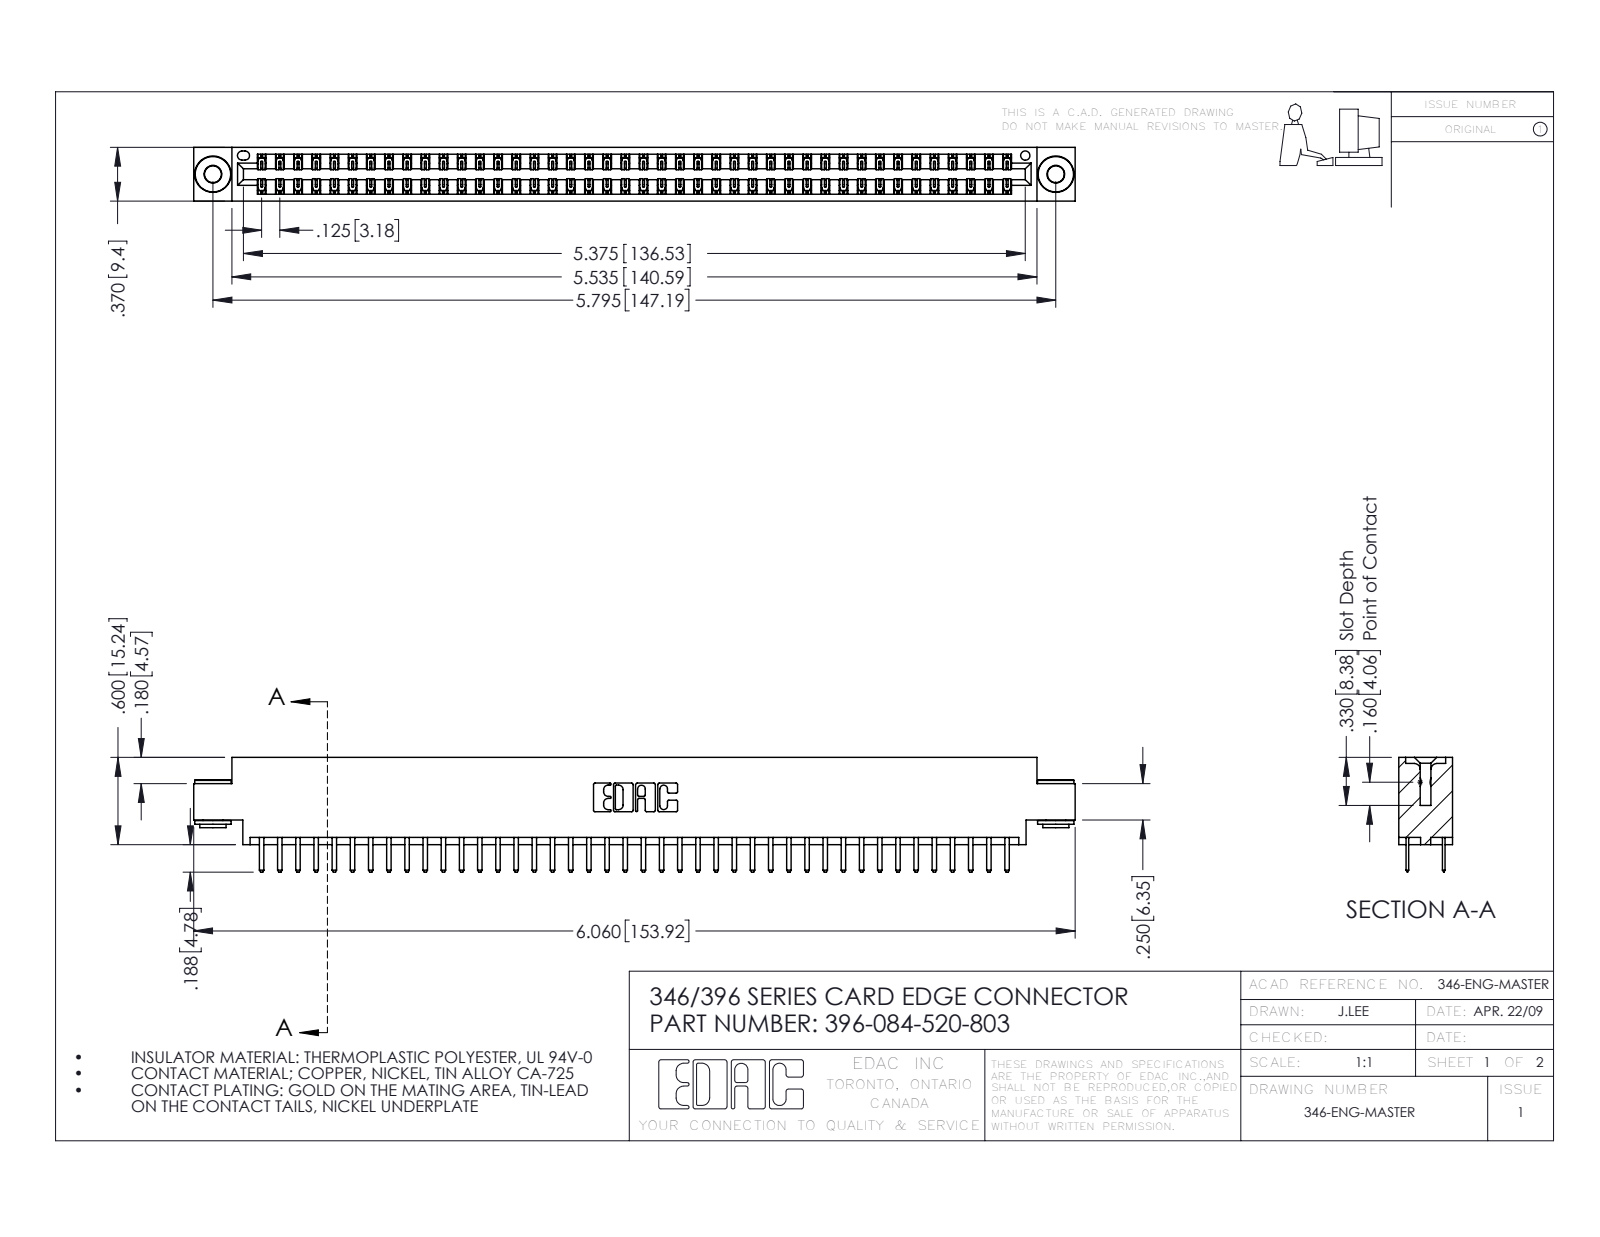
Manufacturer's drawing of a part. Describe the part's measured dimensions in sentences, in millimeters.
The part is named "345-250-002_345-250-002-102; 346 Part_0.170 Offset - 0.156 Dia-TH; 396-084-520-803; 345-292-001_345-293-120". Its 3-D file was written by "SolidWorks 2016 (CONFIG_CONTROL_DESIGN)". It is 87 solids with 4868 faces: 3198 planar, 1662 cylindrical and 8 other. Overall it measures 153.9 by 20 by 9.4 millimeters. Its volume is 14 800 cubic millimeters and its surface area 20 700 square millimeters. Round holes: 2 of diameter 2.9, 2 of diameter 4, 1 of diameter 1.6. Round bosses or shafts: 2 of diameter 6.4, 2 of diameter 4.6, 2 of diameter 3.5. Partial cylindrical surfaces (rounded edges, fillets, slot ends): 126 of radius 0.2, 88 of radius 0.3, 22 of radius 0.3, 6 of radius 0.2, 6 of radius 0.8, 3 of radius 0.7, 2 of radius 0.4, 2 of radius 0.6. The main face-to-face distances are 1.2, 8.2, 6.4, 9.4, 0.6, 7, 1.8, 7.6, 3.8, 5.6. The hole center spacings are 6.2, 141.9, 147.2.
